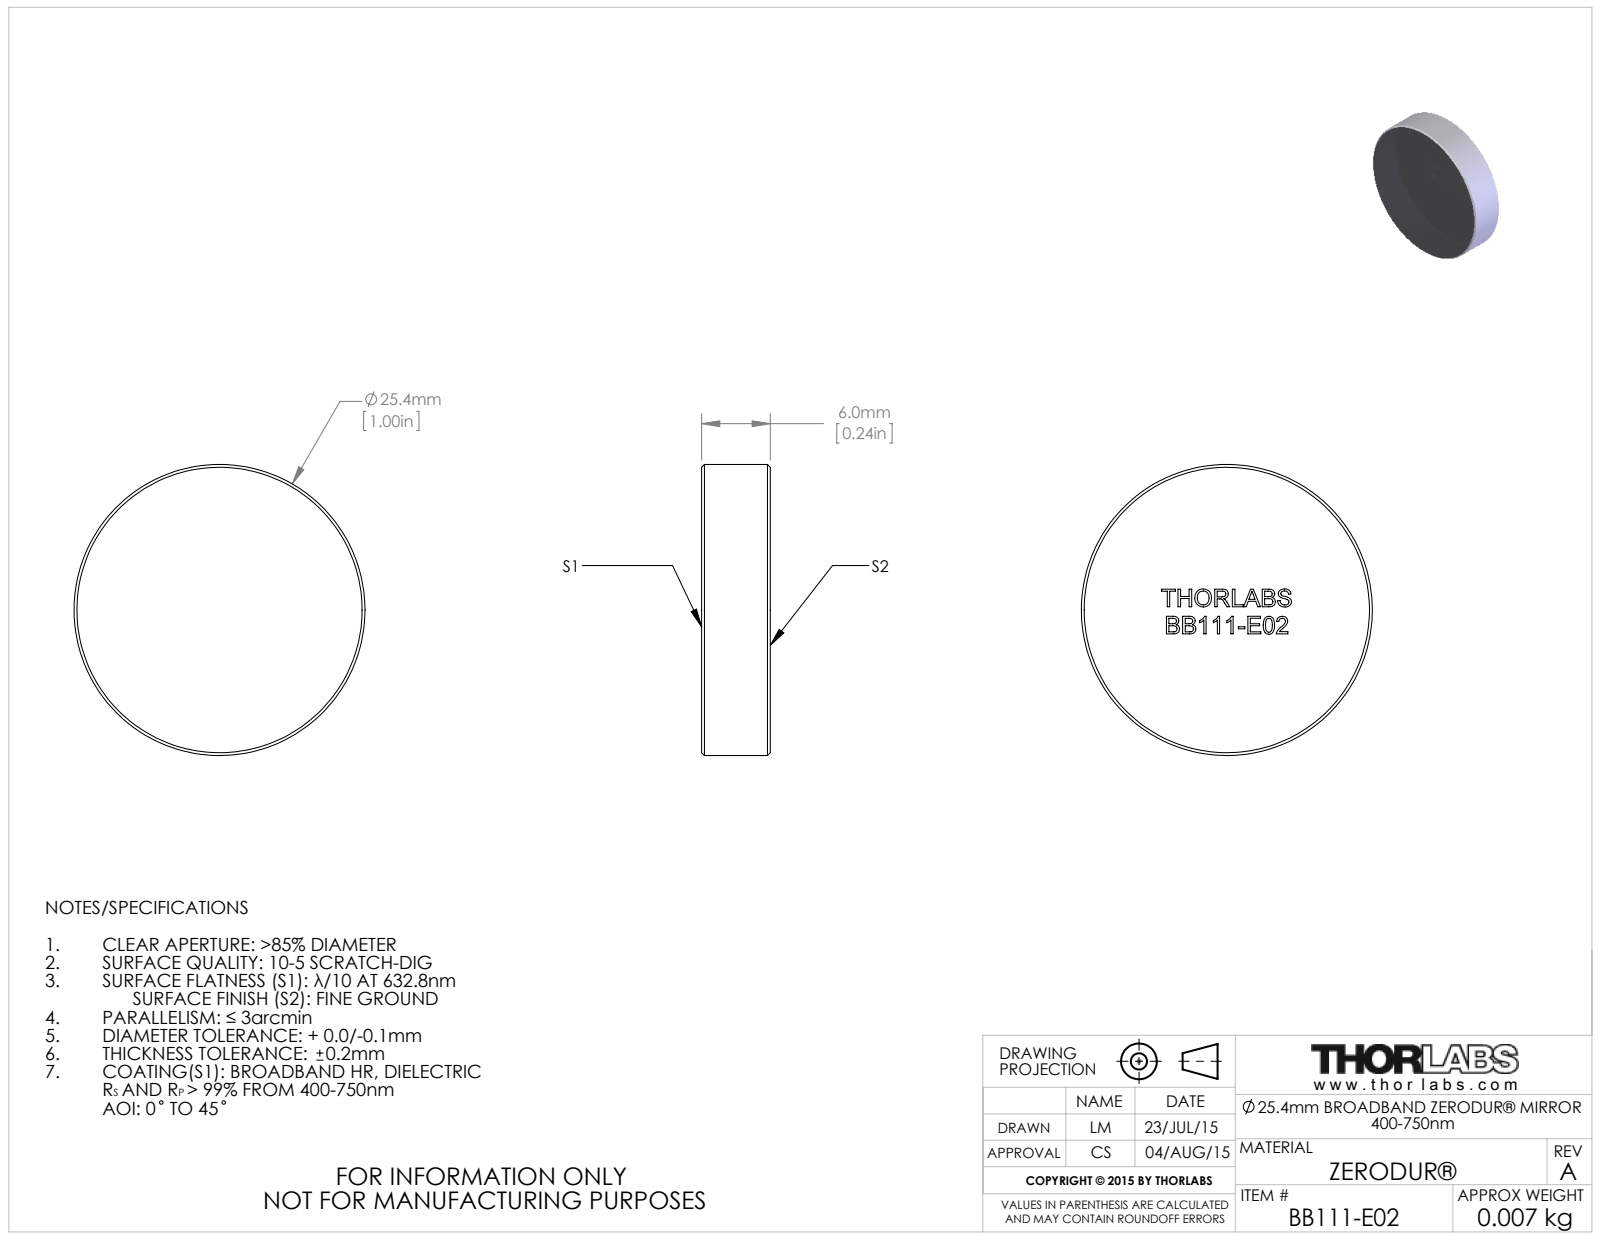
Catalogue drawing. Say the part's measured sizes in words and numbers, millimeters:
The part is named "TTN045196-E0W". Its 3-D file was written by "SolidWorks 2014 (CONFIG_CONTROL_DESIGN)". It is 1 solid with 234 faces: 141 planar, 2 cylindrical and 91 other. Overall it measures 25.4 by 25.4 by 6 millimeters. Its volume is 3 035 cubic millimeters and its surface area 1 469 square millimeters. Round bosses or shafts: 1 of diameter 25.4. The main face-to-face distances are 6, 2.37, 1.36, 1.54, 1.19, 1.18, 3.02, 1.92, 0.83, 5.69.
